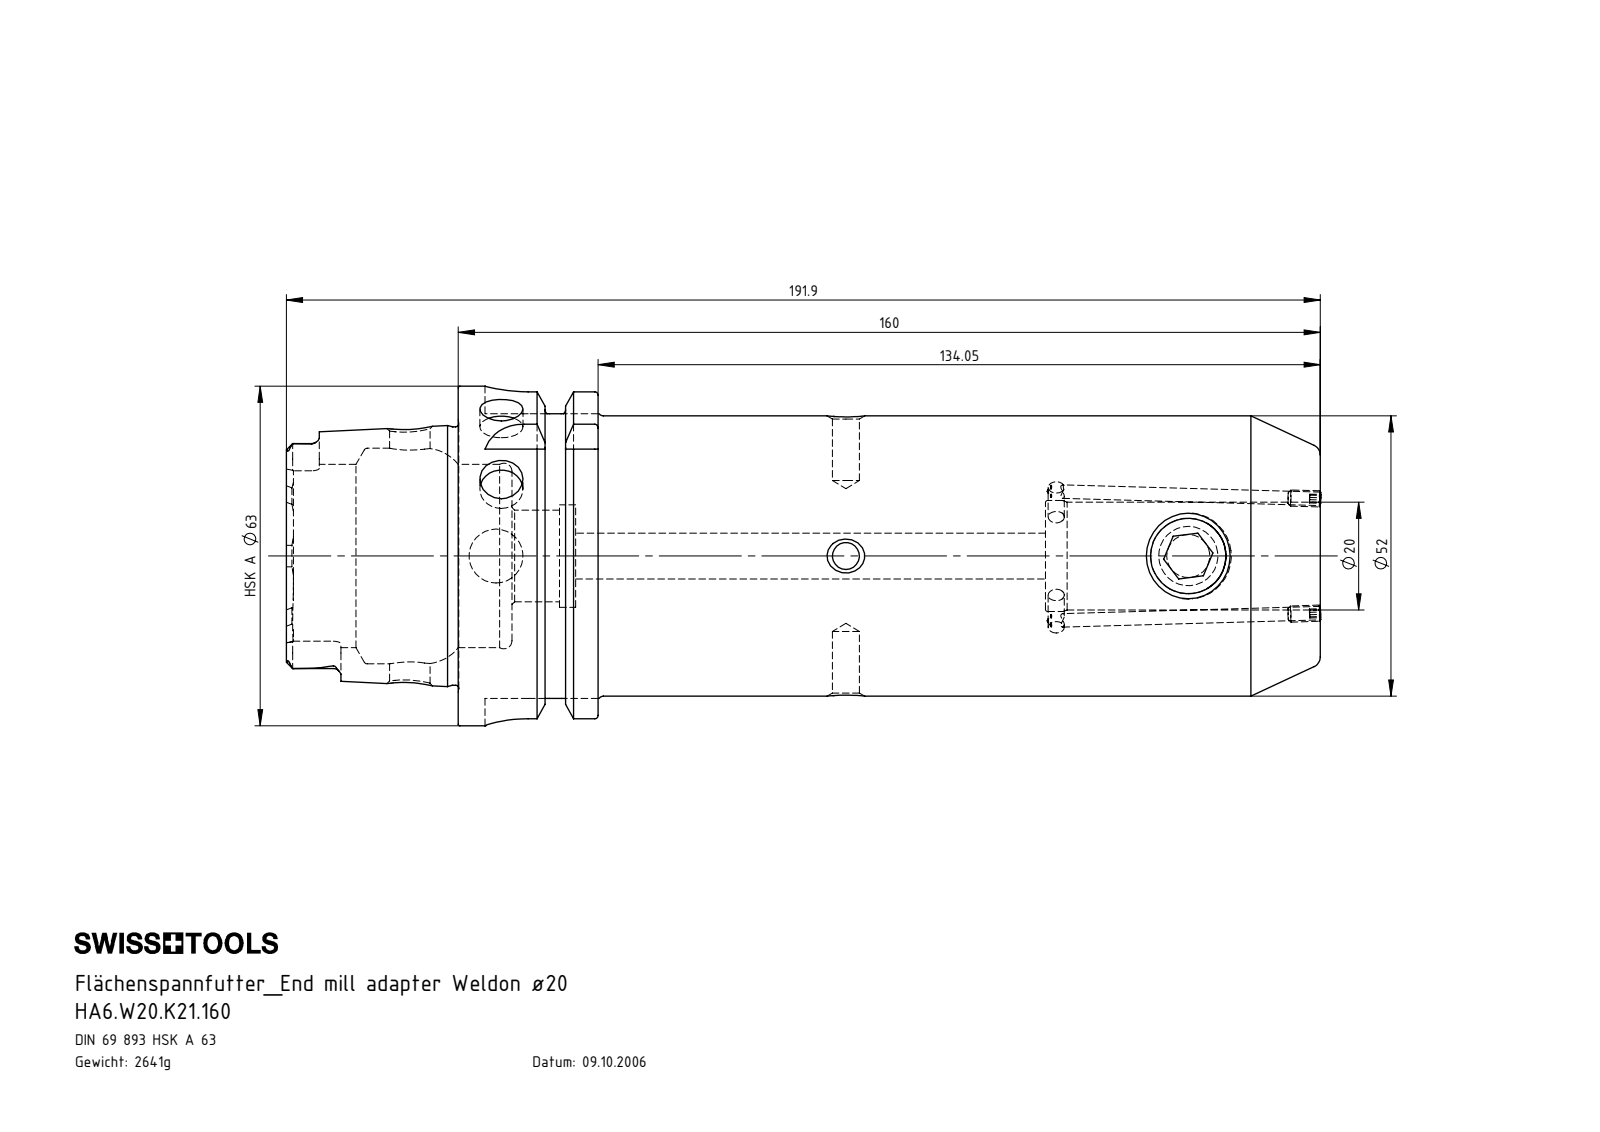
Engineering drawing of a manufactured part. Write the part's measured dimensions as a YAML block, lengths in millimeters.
part_name: "HA6.W20.K21.160; ERU-CJ2.001.006; W20-ER1.001.016; HA6-W20.K21.160_D_Fertigbearbeitung"
step_written_by: "SolidWorks 2012 (CONFIG_CONTROL_DESIGN)"
units: millimeters
bodies: {solids: 4, faces: 287, planar: 78, cylindrical: 81, other: 128}
overall_size: [191.98, 63, 63]
volume: 336395
surface_area: 52469
round_holes:
  - {diameter: 2.5, count: 2}
  - {diameter: 5, count: 2}
  - {diameter: 8, count: 2}
  - {diameter: 3, count: 1}
  - {diameter: 7.5, count: 1}
  - {diameter: 8.5, count: 1}
  - {diameter: 10, count: 1}
  - {diameter: 14, count: 1}
  - {diameter: 17, count: 1}
  - {diameter: 19, count: 1}
  - {diameter: 20, count: 1}
  - {diameter: 20.6, count: 1}
round_bosses_or_shafts:
  - {diameter: 3, count: 2}
  - {diameter: 63, count: 1}
  - {diameter: 54.95, count: 1}
  - {diameter: 52, count: 1}
  - {diameter: 47.94, count: 1}
  - {diameter: 16, count: 1}
partial_cylinders:
  - {radius: 1.4, count: 6}
  - {radius: 2.88, count: 4}
  - {radius: 8, count: 4}
face_to_face_distances: [160, 25.95, 134.05, 16, 9.95, 150.05, 31.9, 41.85, 57.85, 191.9]
hole_center_spacings: [63.55, 64.95, 80.95, 128.5]
